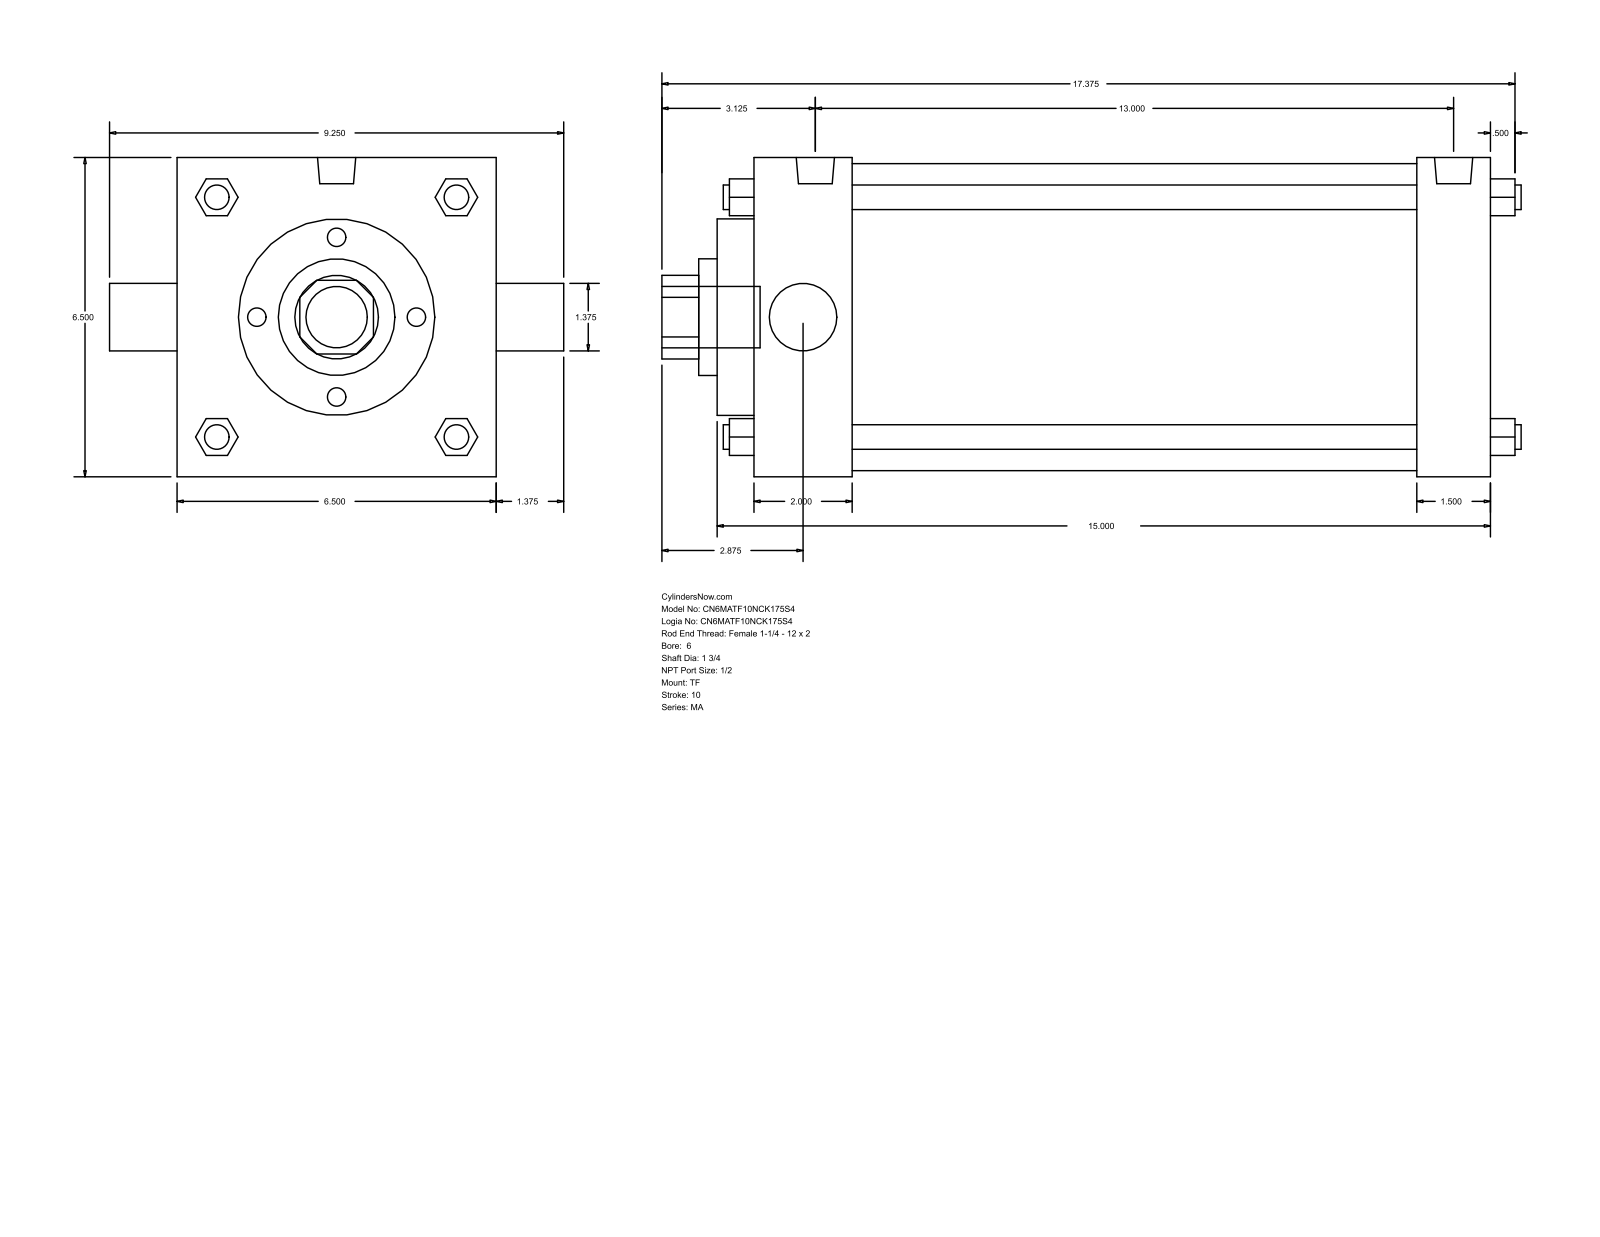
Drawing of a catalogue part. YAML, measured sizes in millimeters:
part_name: "MA_TF__0600_1.75"
step_written_by: "GSSL Pune (CONFIG_CONTROL_DESIGN)"
units: millimeters
bodies: {solids: 0, faces: 122, planar: 93, cylindrical: 29, other: 0}
overall_size: [444.5, 234.95, 165.1]
round_holes:
  - {diameter: 34.92, count: 1}
  - {diameter: 44.45, count: 1}
  - {diameter: 60.33, count: 1}
  - {diameter: 101.6, count: 1}
  - {diameter: 158.75, count: 1}
round_bosses_or_shafts:
  - {diameter: 12.7, count: 4}
  - {diameter: 17.46, count: 3}
  - {diameter: 19.77, count: 2}
  - {diameter: 31.75, count: 1}
partial_cylinders:
  - {radius: 21.63, count: 1}
face_to_face_distances: [165.1, 381, 19.05, 50.8, 342.9, 38.1, 330.2, 292.1, 69.85, 361.95]
